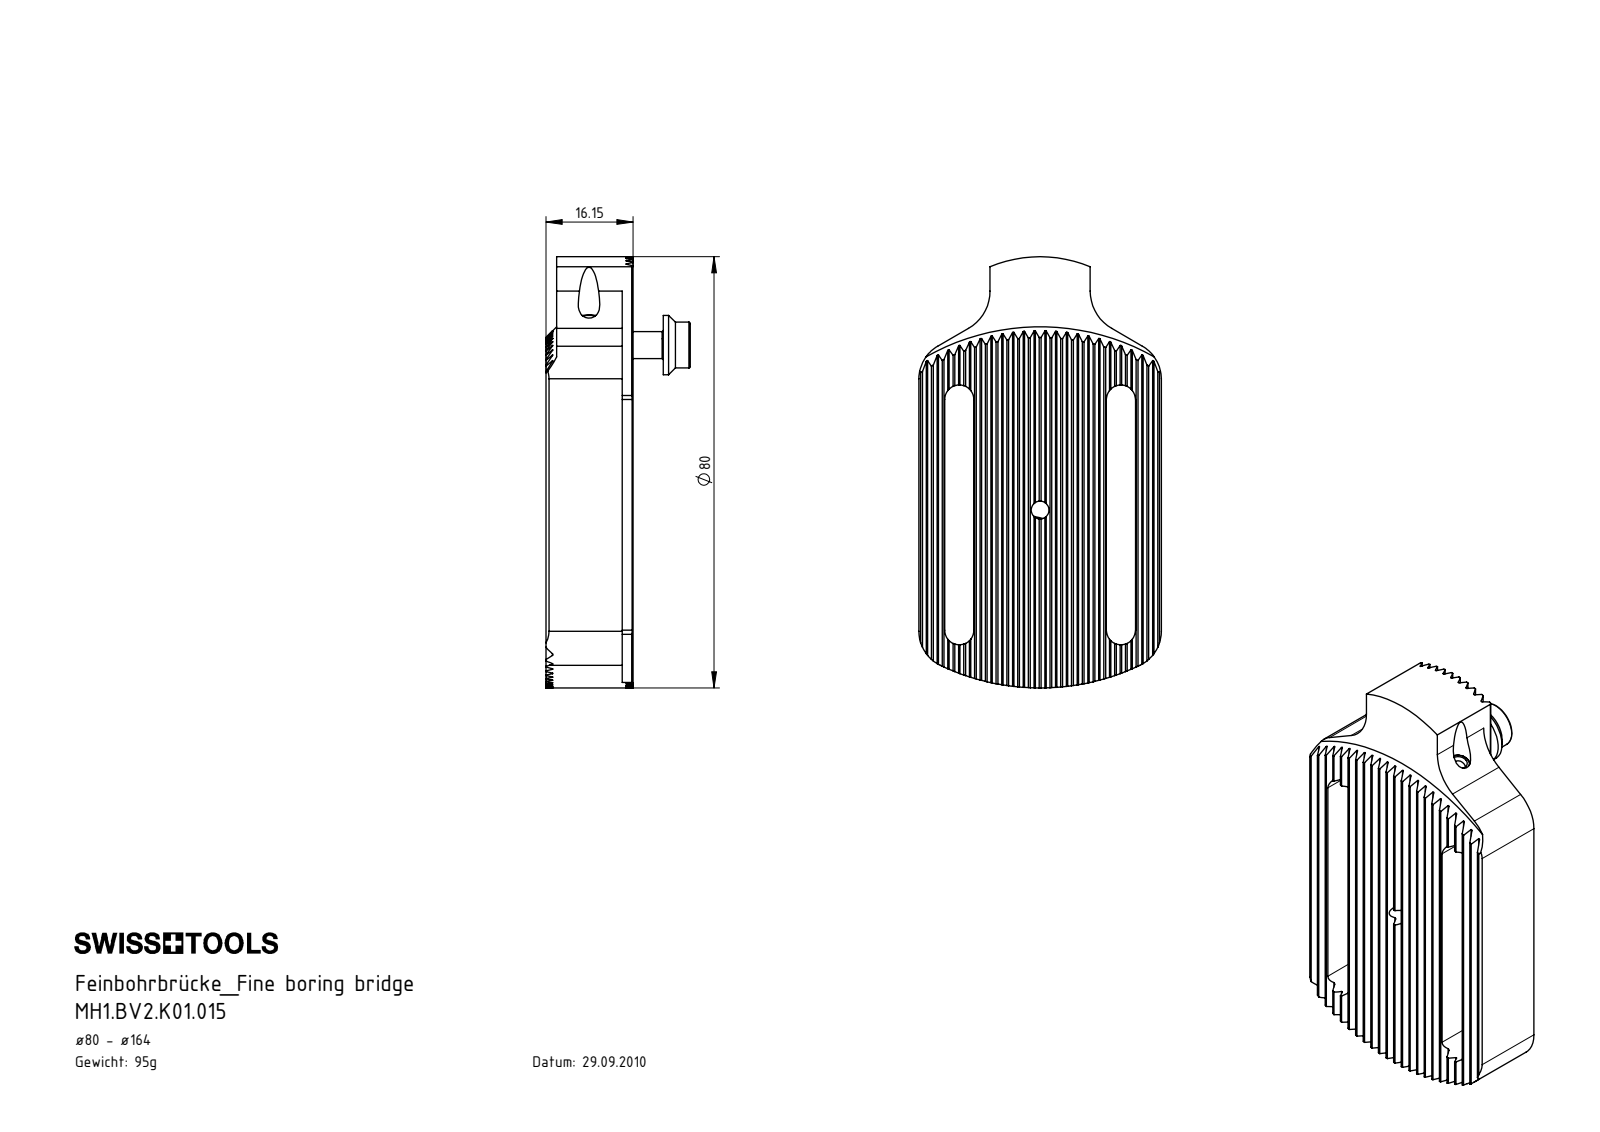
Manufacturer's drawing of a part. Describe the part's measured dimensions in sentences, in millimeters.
The part is named "MH1.BV2.K01.015; ISO 4026 - M4 x 5; BN 1392 - M5 x 16; MH1-BV2.K01.015_C". Its 3-D file was written by "SolidWorks 2017 (AUTOMOTIVE_DESIGN)". It is 4 solids with 582 faces: 363 planar, 118 cylindrical and 101 other. Overall it measures 80 by 45 by 26.78 millimeters. Its volume is 33 129 cubic millimeters and its surface area 16 319 square millimeters. Round holes: 3 of diameter 4.2, 2 of diameter 3.3, 2 of diameter 5.5, 1 of diameter 2. Round bosses or shafts: 2 of diameter 11, 2 of diameter 8.5, 2 of diameter 5, 1 of diameter 4. Partial cylindrical surfaces (rounded edges, fillets, slot ends): 31 of radius 0.14, 4 of radius 2.7, 4 of radius 5.75, 4 of radius 7, 2 of radius 1.25, 2 of radius 8, 1 of radius 24, 1 of radius 43. The main face-to-face distances are 1.73, 8.66, 3.46, 6.93, 5.2, 5.77, 10.39, 30, 3.05, 8.45. The hole center spacings are 7.87, 20.4, 27.89, 30.6, 47.91, 51.
